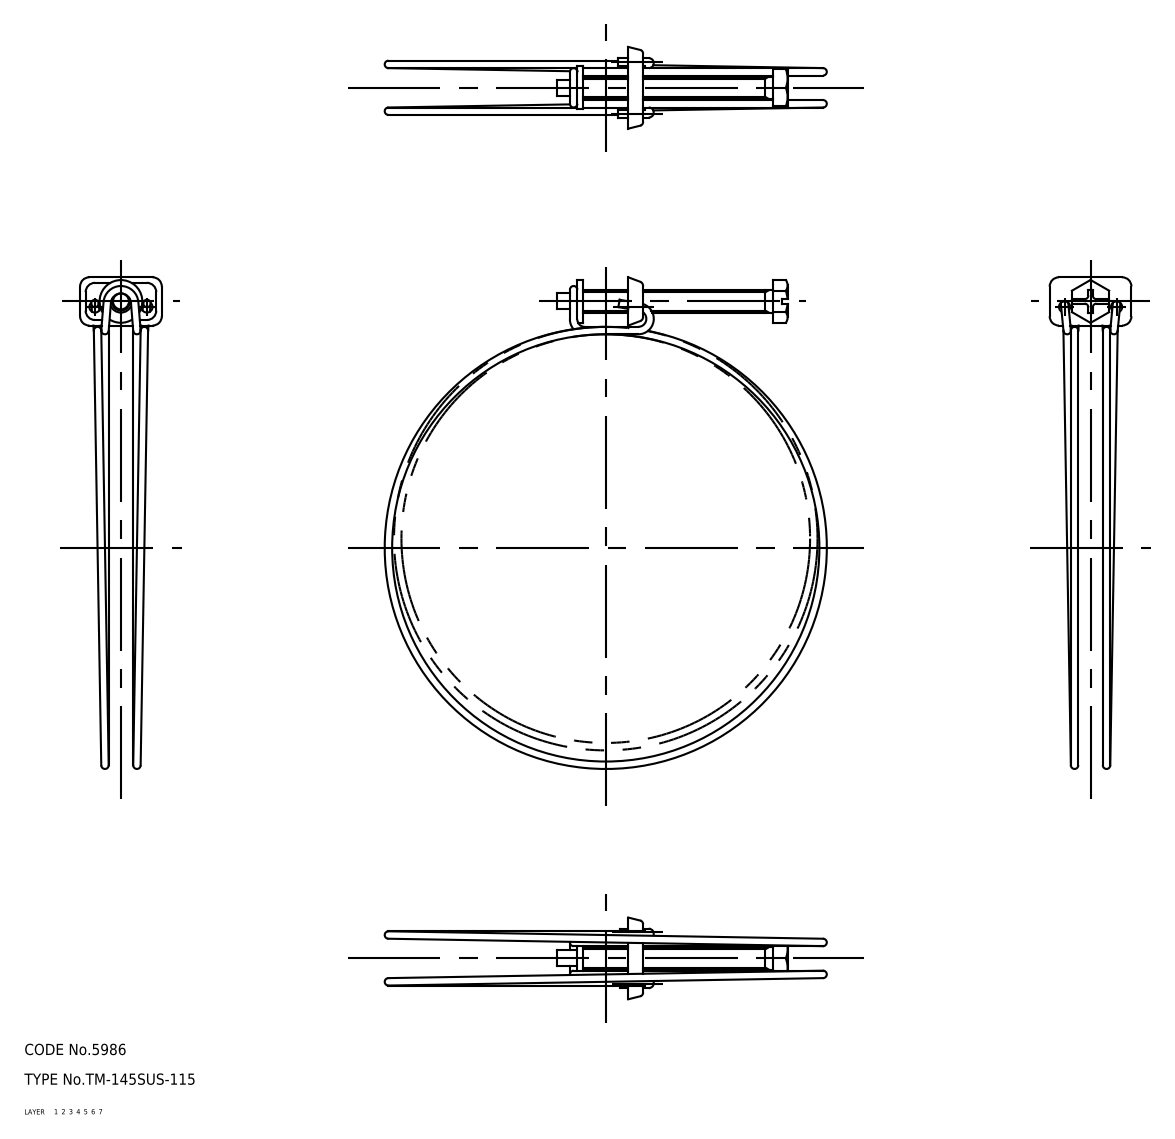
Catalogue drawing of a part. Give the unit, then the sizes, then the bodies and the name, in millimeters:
Units: millimetres
Overall size (bounding box): 132.35 × 119 × 22
Volume: 5 089 mm³ · Surface area: 7 585 mm²
Bodies: 3 solids, 119 faces (0 planar, 0 cylindrical, 119 other)
Part name (STEP PRODUCT): screw; holder; band; TM_145SUS_115_21190_36
STEP written by: CADfix (AUTOMOTIVE_DESIGN)
